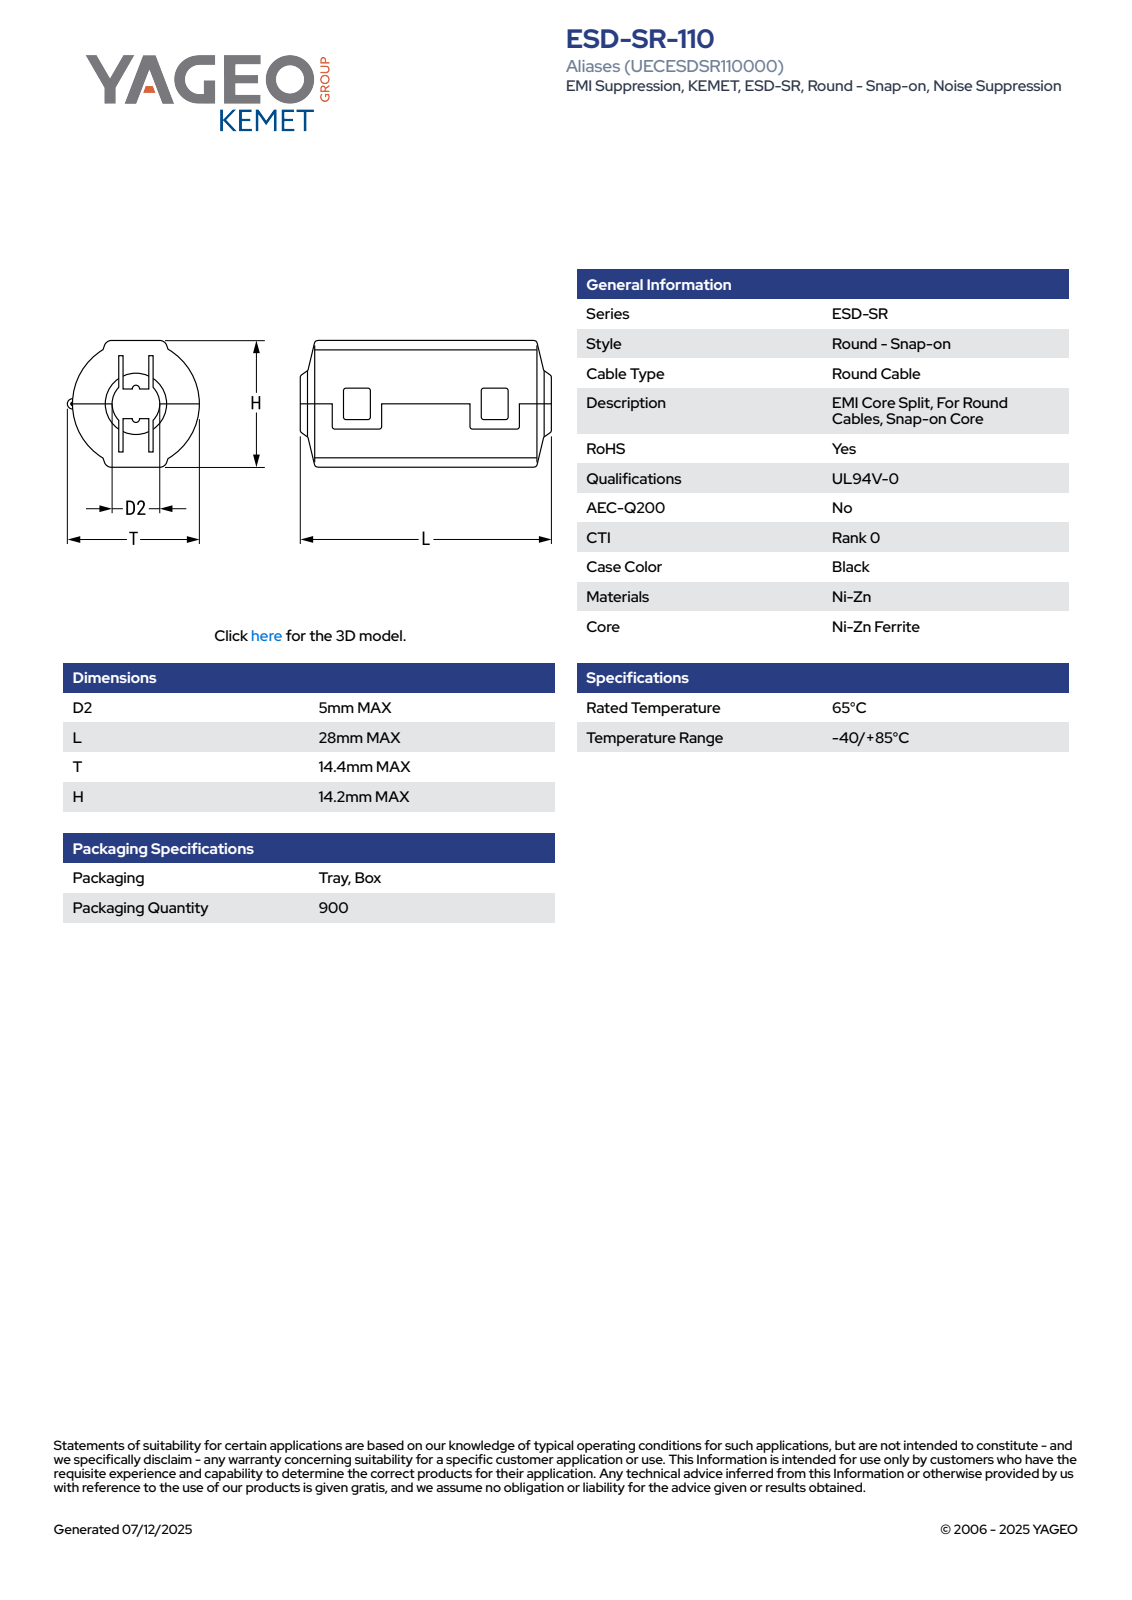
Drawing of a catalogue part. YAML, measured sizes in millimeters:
part_name: "EC_ESDSR_D25L28T14.4H14.2"
step_written_by: "SolidWorks 2014 (AUTOMOTIVE_DESIGN)"
units: millimeters
bodies: {solids: 1, faces: 92, planar: 72, cylindrical: 6, other: 14}
overall_size: [28, 14.4, 14.21]
volume: 4143
surface_area: 2031
partial_cylinders:
  - {radius: 2.89, count: 2}
  - {radius: 7.2, count: 1}
face_to_face_distances: [14.2, 5.27, 8.93, 11.41, 3.66, 28, 2.25, 25.75, 23.5, 4.2]
